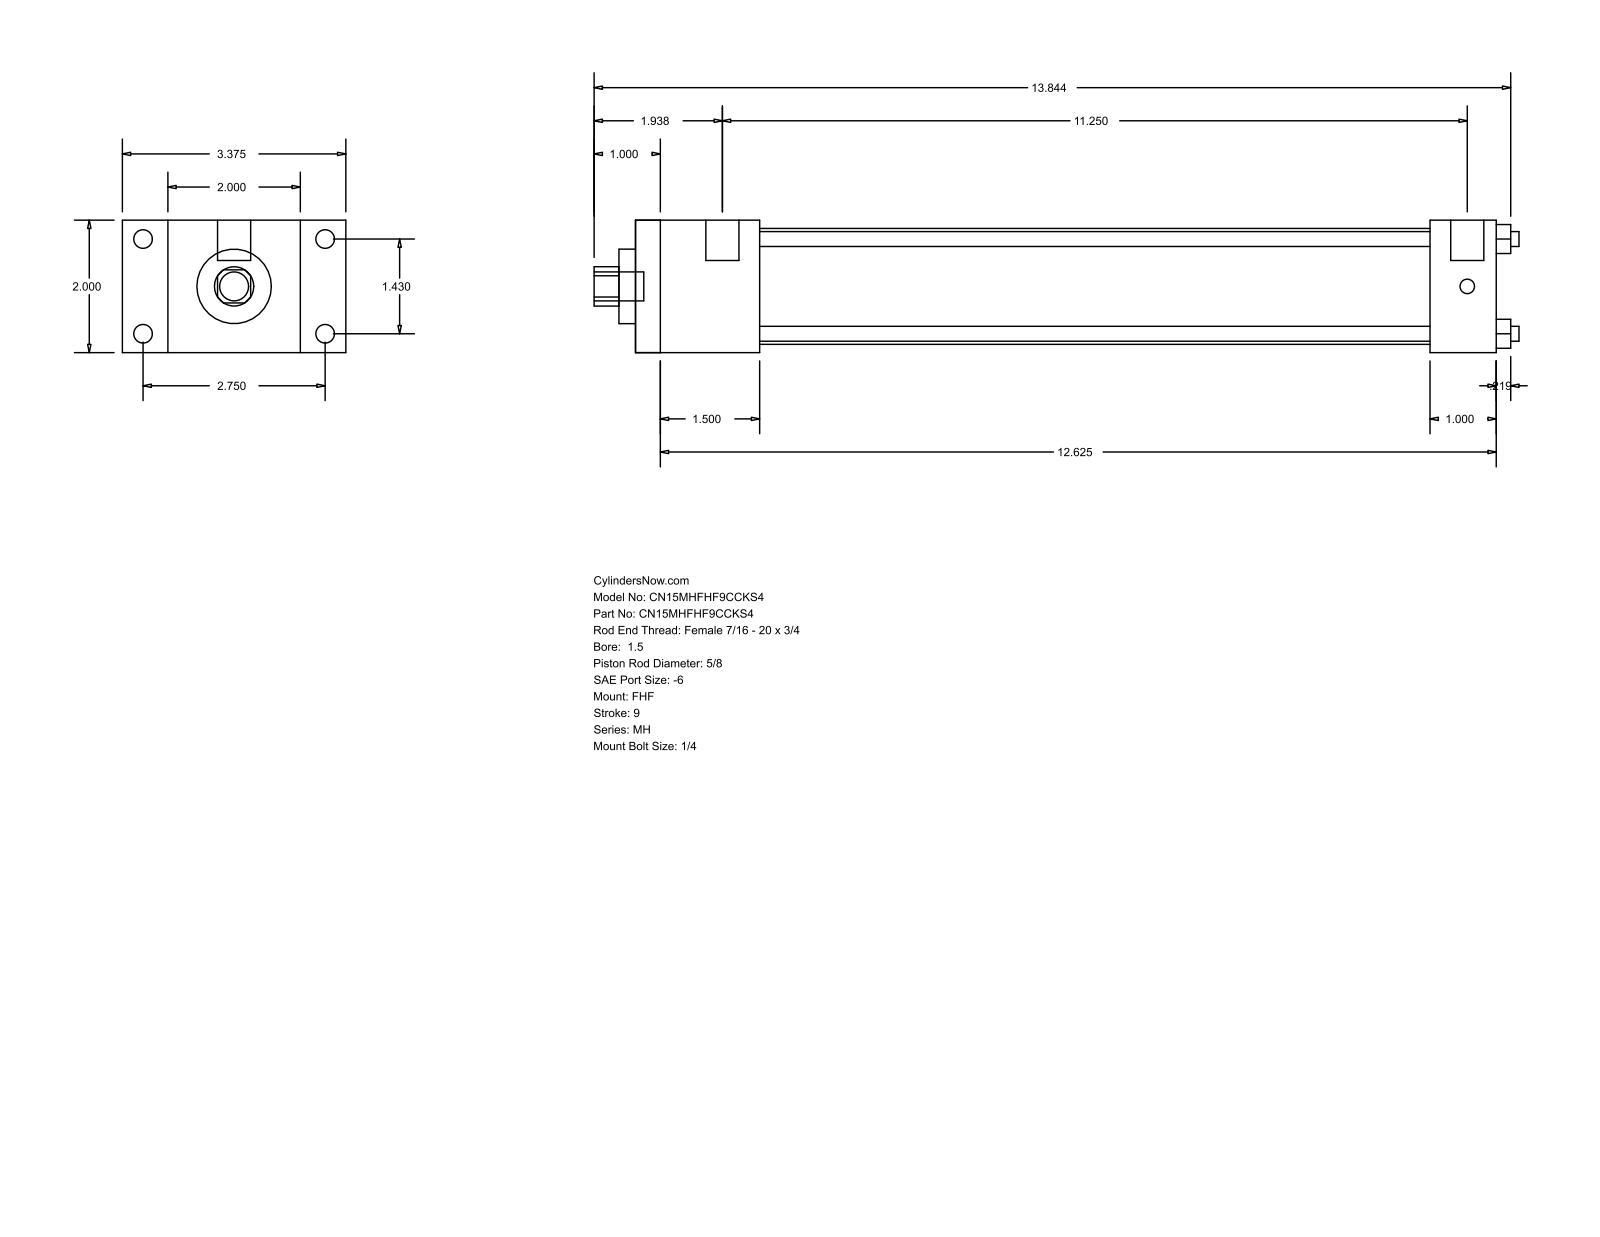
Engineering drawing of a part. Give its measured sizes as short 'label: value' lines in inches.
name: MH_FHF__0150_0.625
written by: GSSL Pune (CONFIG_CONTROL_DESIGN)
unit: in
bodies: 0 solids, 88 faces (60 planar, 28 cylindrical, 0 other)
size: 13.969 × 3.375 × 2
holes: 4× ⌀0.225, 1× ⌀0.625, 1× ⌀1.125, 1× ⌀1.75
bosses: 4× ⌀0.281, 4× ⌀0.219, 2× ⌀0.5, 1× ⌀0.437
rounds: 1× R0.297
face distances: 2, 0.687, 2.687, 1.875, 3.375, 13, 11.125, 12, 10.125, 1
hole spacings: 1.011, 1.43, 2.022
